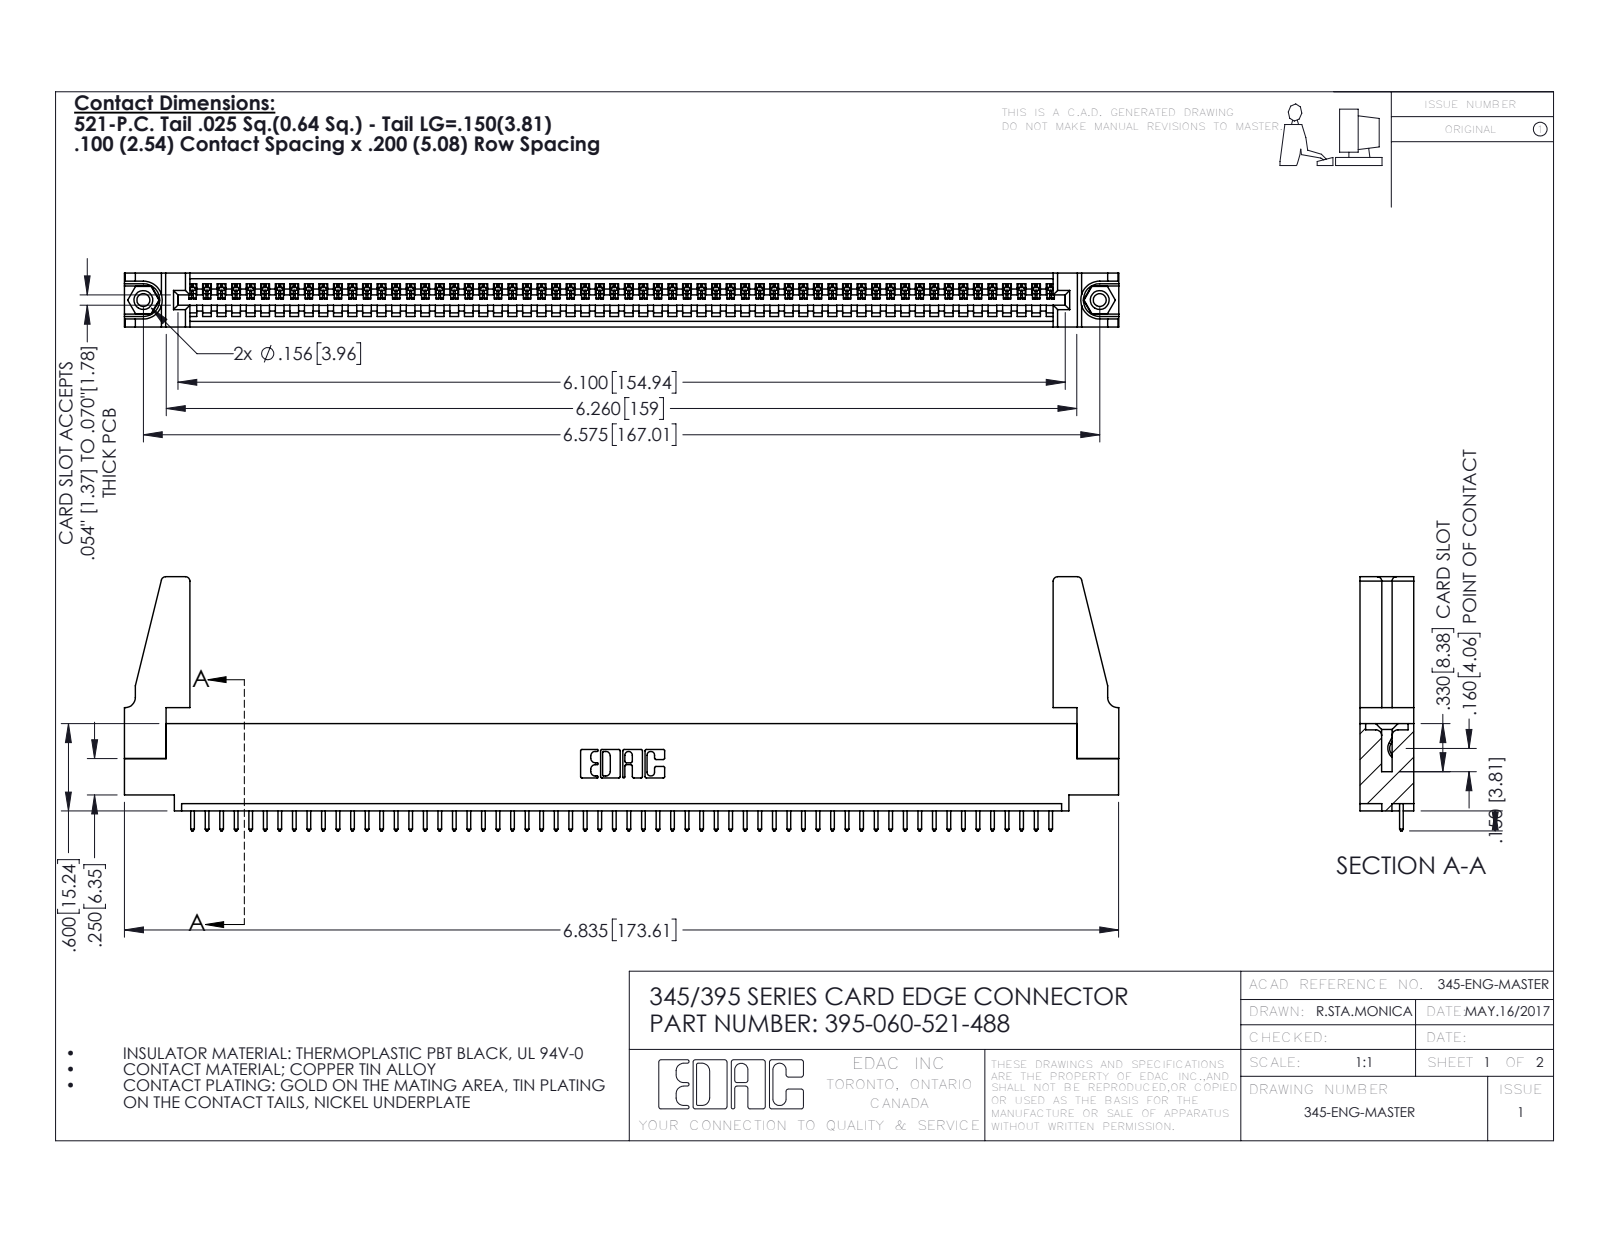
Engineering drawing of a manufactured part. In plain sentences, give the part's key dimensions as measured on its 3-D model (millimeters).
The part is named "395-060-521-488; 345-220-078_345-220-088; 345 Part_0.110 Offset - 0.156 Dia-TH; 345-250-001_345-250-001-102 (+1 more)". Its 3-D file was written by "SolidWorks 2016 (CONFIG_CONTROL_DESIGN)". It is 65 solids with 3734 faces: 2556 planar, 1162 cylindrical and 16 other. Overall it measures 173.6 by 44.4 by 9.4 millimeters. Its volume is 19 650 cubic millimeters and its surface area 24 570 square millimeters. Round holes: 2 of diameter 2.3, 2 of diameter 3.2, 2 of diameter 4, 1 of diameter 1.6. Round bosses or shafts: 2 of diameter 3.9. Partial cylindrical surfaces (rounded edges, fillets, slot ends): 120 of radius 0.2, 120 of radius 0.3, 22 of radius 0.3, 8 of radius 0.8, 6 of radius 0.2, 6 of radius 0.8, 3 of radius 0.7, 2 of radius 0.8. The main face-to-face distances are 1.8, 7.6, 9.4, 5.1, 2.5, 6.9, 0.6, 5.7, 3.8, 1.8. The hole center spacings are 6.9, 161, 167.
